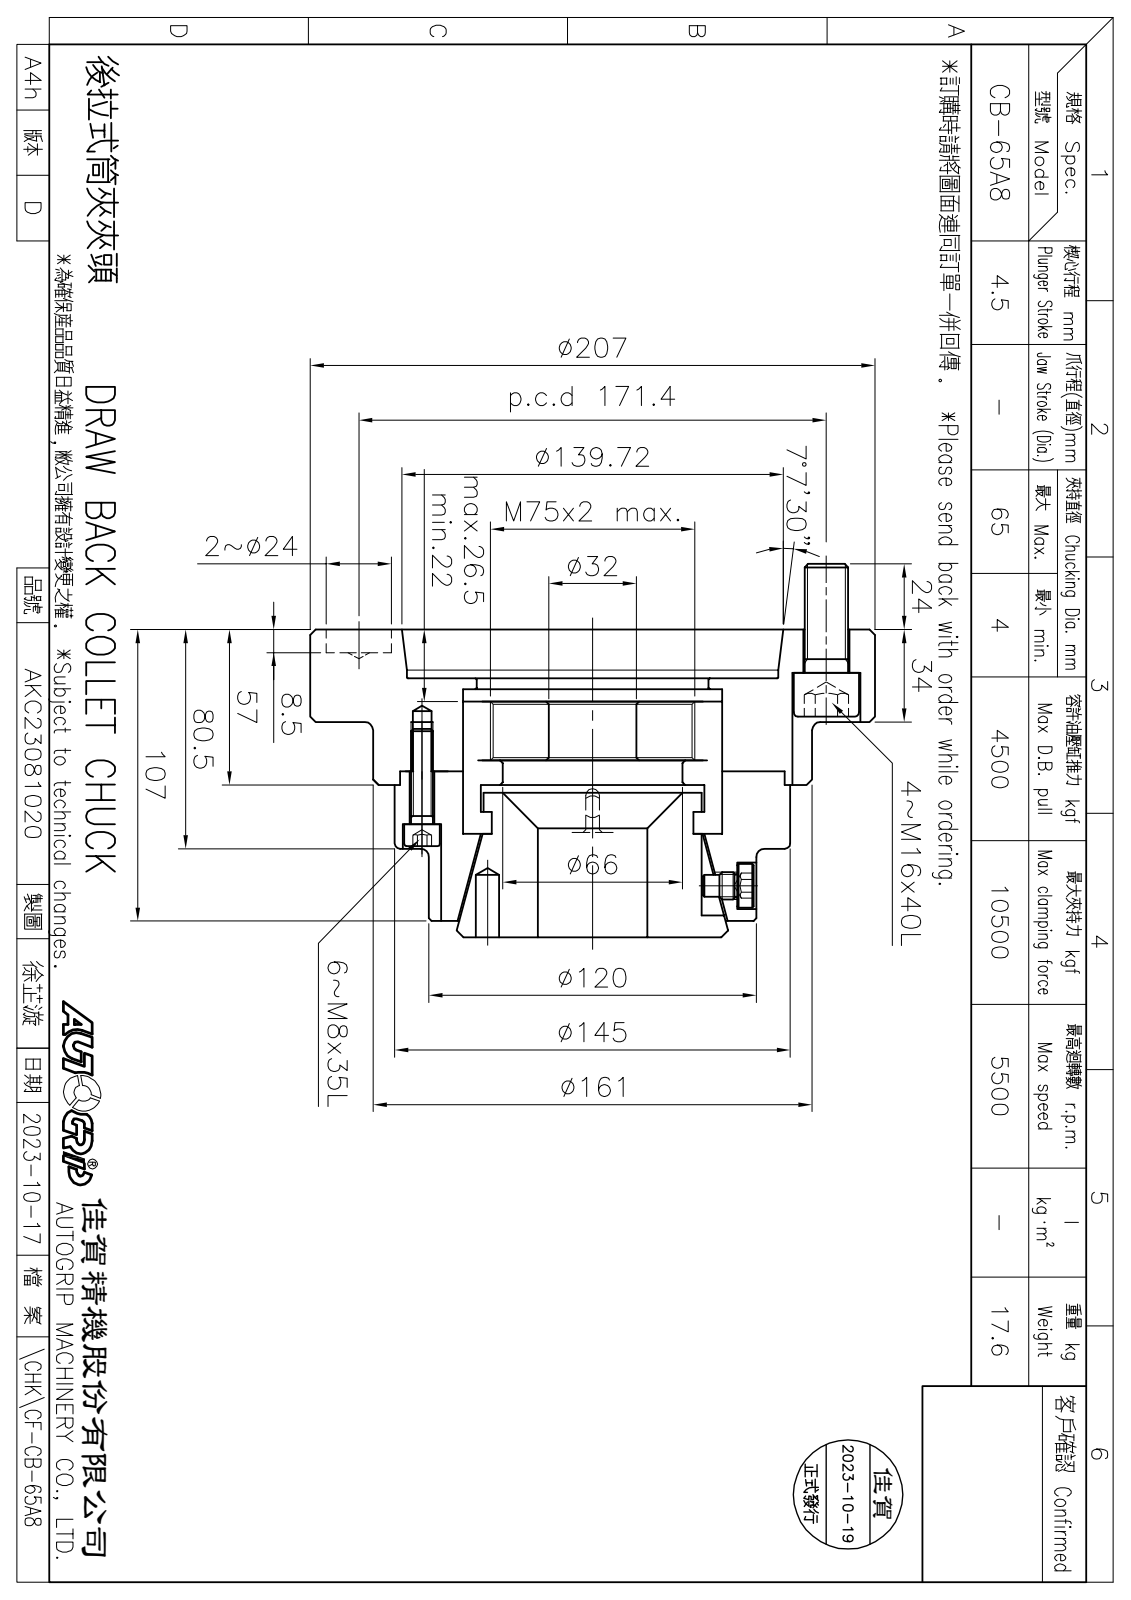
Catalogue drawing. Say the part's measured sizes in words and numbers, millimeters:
The part is named "圓頭內六角螺栓_M8x35; CF-CB-65A8; CF-CB-65-02010; 圓頭內六角螺栓_M16x40 (+3 more)". Its 3-D file was written by "SolidWorks 2020 (CONFIG_CONTROL_DESIGN)". It is 14 solids with 522 faces: 194 planar, 177 cylindrical and 151 other. Overall it measures 207 by 207 by 137 millimeters. Its volume is 1 762 000 cubic millimeters and its surface area 291 608 square millimeters. Round holes: 6 of diameter 6.8, 6 of diameter 8.5, 6 of diameter 9, 6 of diameter 14, 5 of diameter 5, 4 of diameter 17, 4 of diameter 25, 2 of diameter 24, 1 of diameter 6, 1 of diameter 40, 1 of diameter 66, 1 of diameter 73. Round bosses or shafts: 6 of diameter 13, 6 of diameter 8, 4 of diameter 24, 4 of diameter 16, 1 of diameter 207, 1 of diameter 161, 1 of diameter 145, 1 of diameter 120. The main face-to-face distances are 18, 34, 52, 16, 6, 57, 23, 20.5, 39, 38.5. The hole center spacings are 62.5, 85.7, 38.5, 60.63, 66.69, 118.42, 30.05, 31.2.
